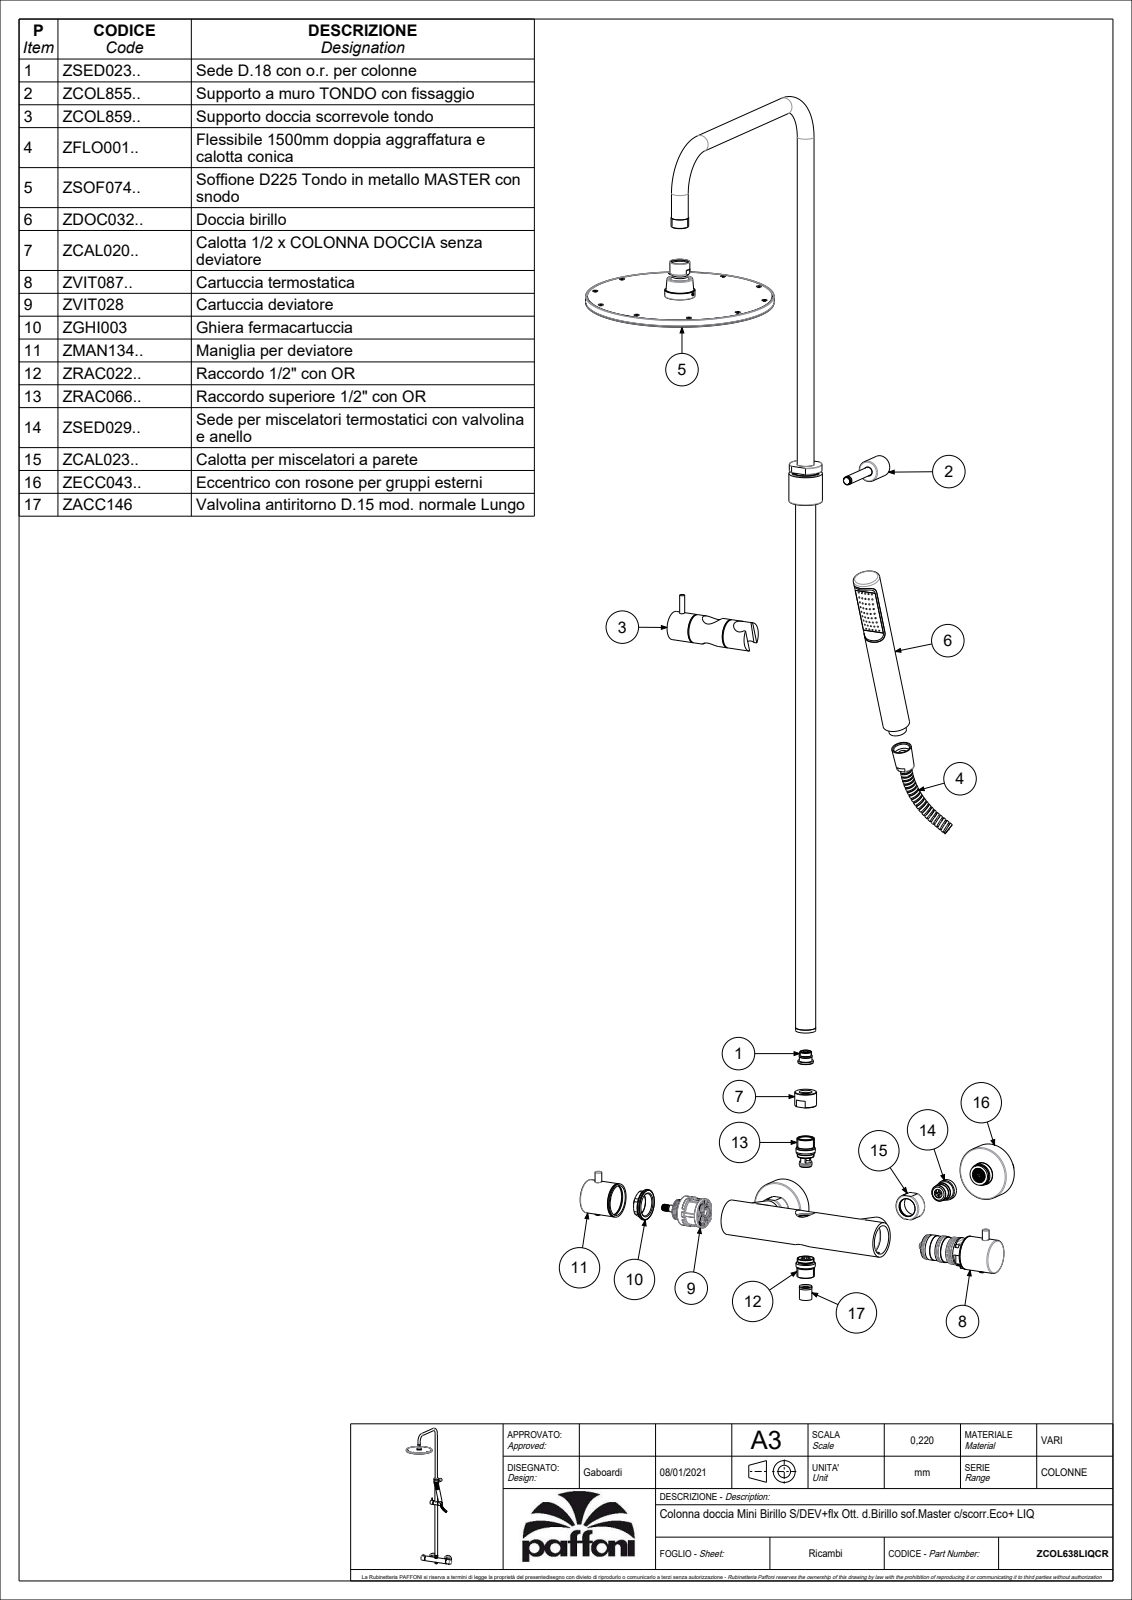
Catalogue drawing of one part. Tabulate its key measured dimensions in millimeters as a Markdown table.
| quantity | value |
| --- | --- |
| part name | ZCOL638LIQCR |
| STEP written by | CREO PARAMETRIC BY PTC INC, 2020044 (CONFIG_CONTROL_DESIGN) |
| units | millimeters |
| bodies | 13 solids, 2832 faces (704 planar, 1430 cylindrical, 698 other) |
| overall size | 1235.1 × 495 × 287.73 |
| volume | 842 965 mm³ |
| surface area | 542 984 mm² |
| round holes (diameter × count) | 0.8 × 324, 1.2 × 80, 1.5 × 45, 4 × 4, 7 × 3, 10.5 × 3, 15.1 × 3, 16 × 3, 17 × 3, 2.5 × 2, 3 × 2, 3.25 × 2 |
| round bosses / shafts (diameter × count) | 40 × 3, 20 × 3, 63.5 × 2, 27 × 2, 26.2 × 2, 23 × 2, 21.2 × 2, 21 × 2 |
| partial cylindrical surfaces (radius × count) | 1.5 × 64, 1 × 6, 1.75 × 4, 6 × 4, 2.75 × 2, 4 × 2, 6.5 × 2, 7.2 × 2 |
| main face-to-face distances | 6.5, 0.6, 3, 42.3, 41.7, 45.3, 44.7, 3.25, 23.8, 88.5 |
| hole center spacings | 7.91, 13.76, 20.01, 6.5, 13, 26.39, 28.16, 90 |
